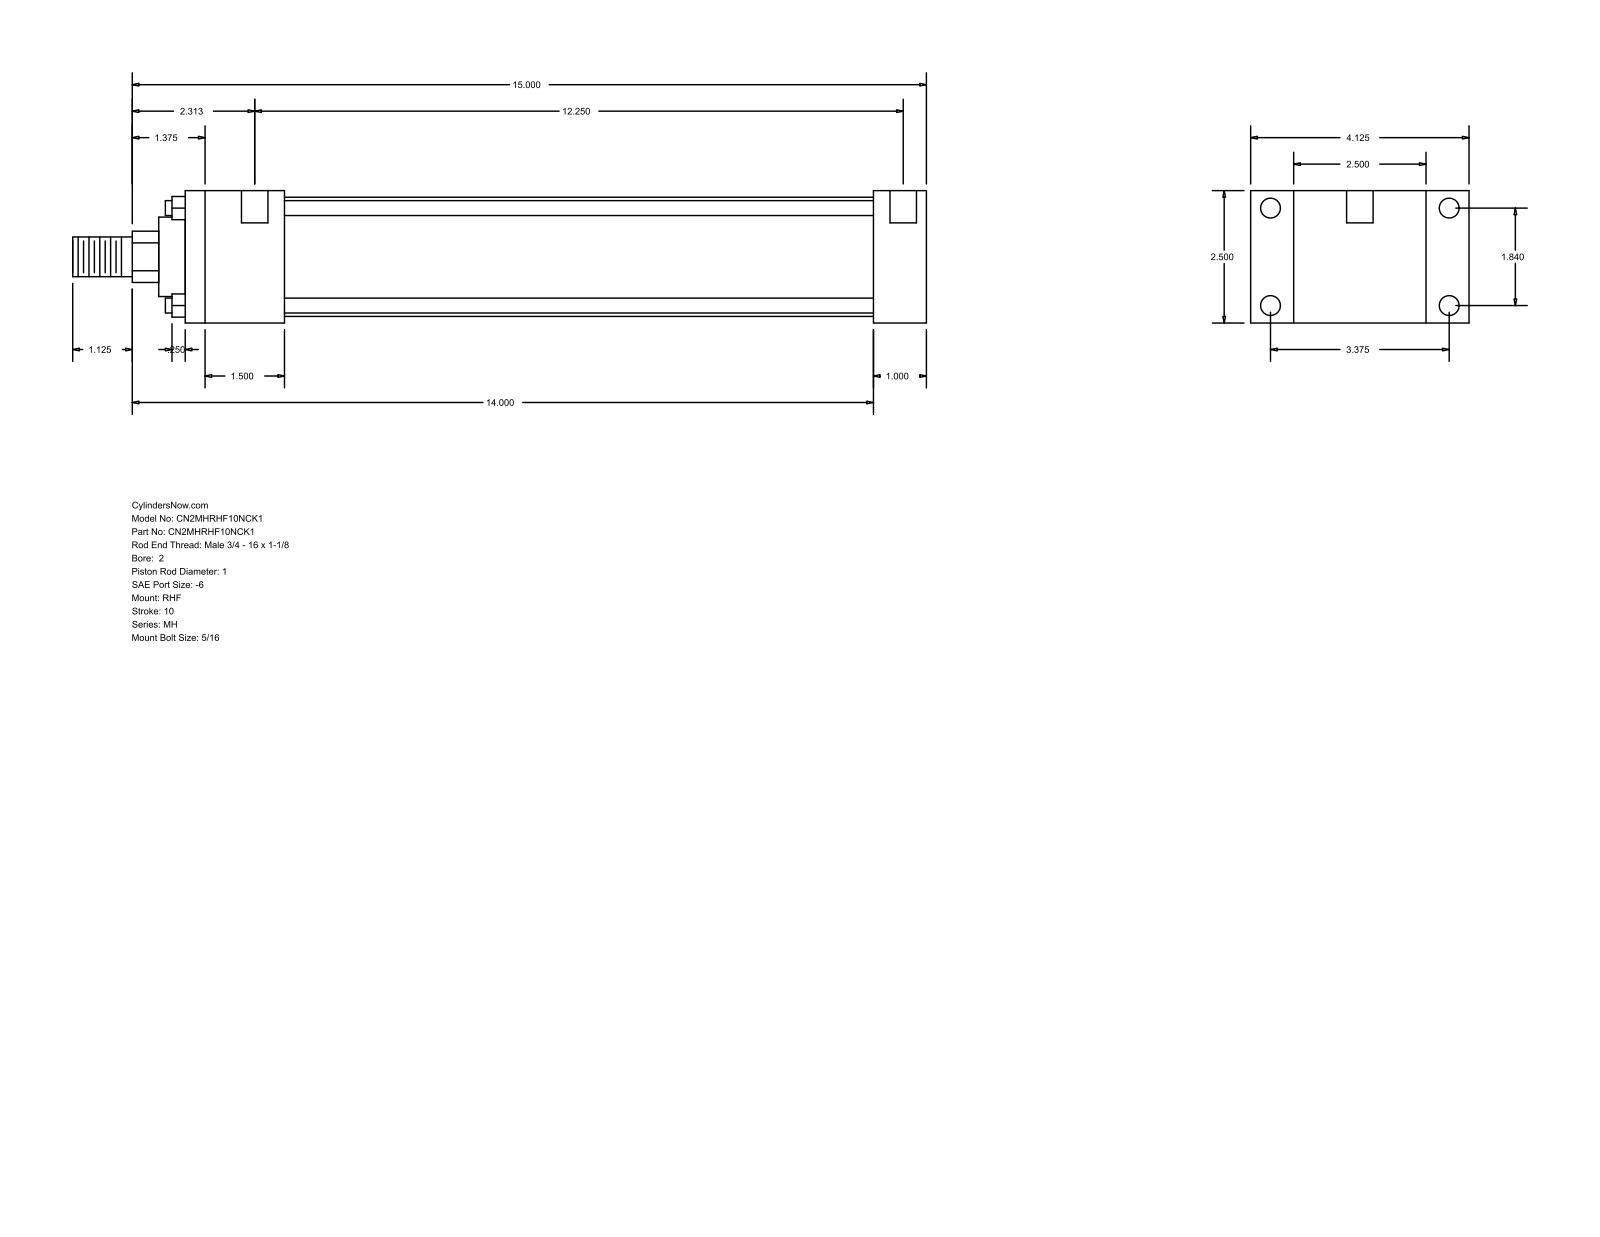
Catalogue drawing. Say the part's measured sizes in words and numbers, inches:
The part is named "MH_RHF__0200_1". Its 3-D file was written by "GSSL Pune (CONFIG_CONTROL_DESIGN)". It is 0 solids with 88 faces: 60 planar, 28 cylindrical and 0 other. Overall it measures 16.125 by 4.125 by 2.5 inches. Round holes: 4 of diameter 0.219, 4 of diameter 0.375, 2 of diameter 0.5. Round bosses or shafts: 4 of diameter 0.281, 1 of diameter 2.25, 1 of diameter 1.5, 1 of diameter 1, 1 of diameter 0.75. Partial cylindrical surfaces (rounded edges, fillets, slot ends): 1 of radius 0.484. The main face-to-face distances are 2.5, 1, 0.813, 3.313, 14, 13, 4.125, 1.875, 11.125, 12.125. The hole center spacings are 1.84, 3.375, 3.844, 12.562, 0.125, 0.187, 12.25, 12.375.
